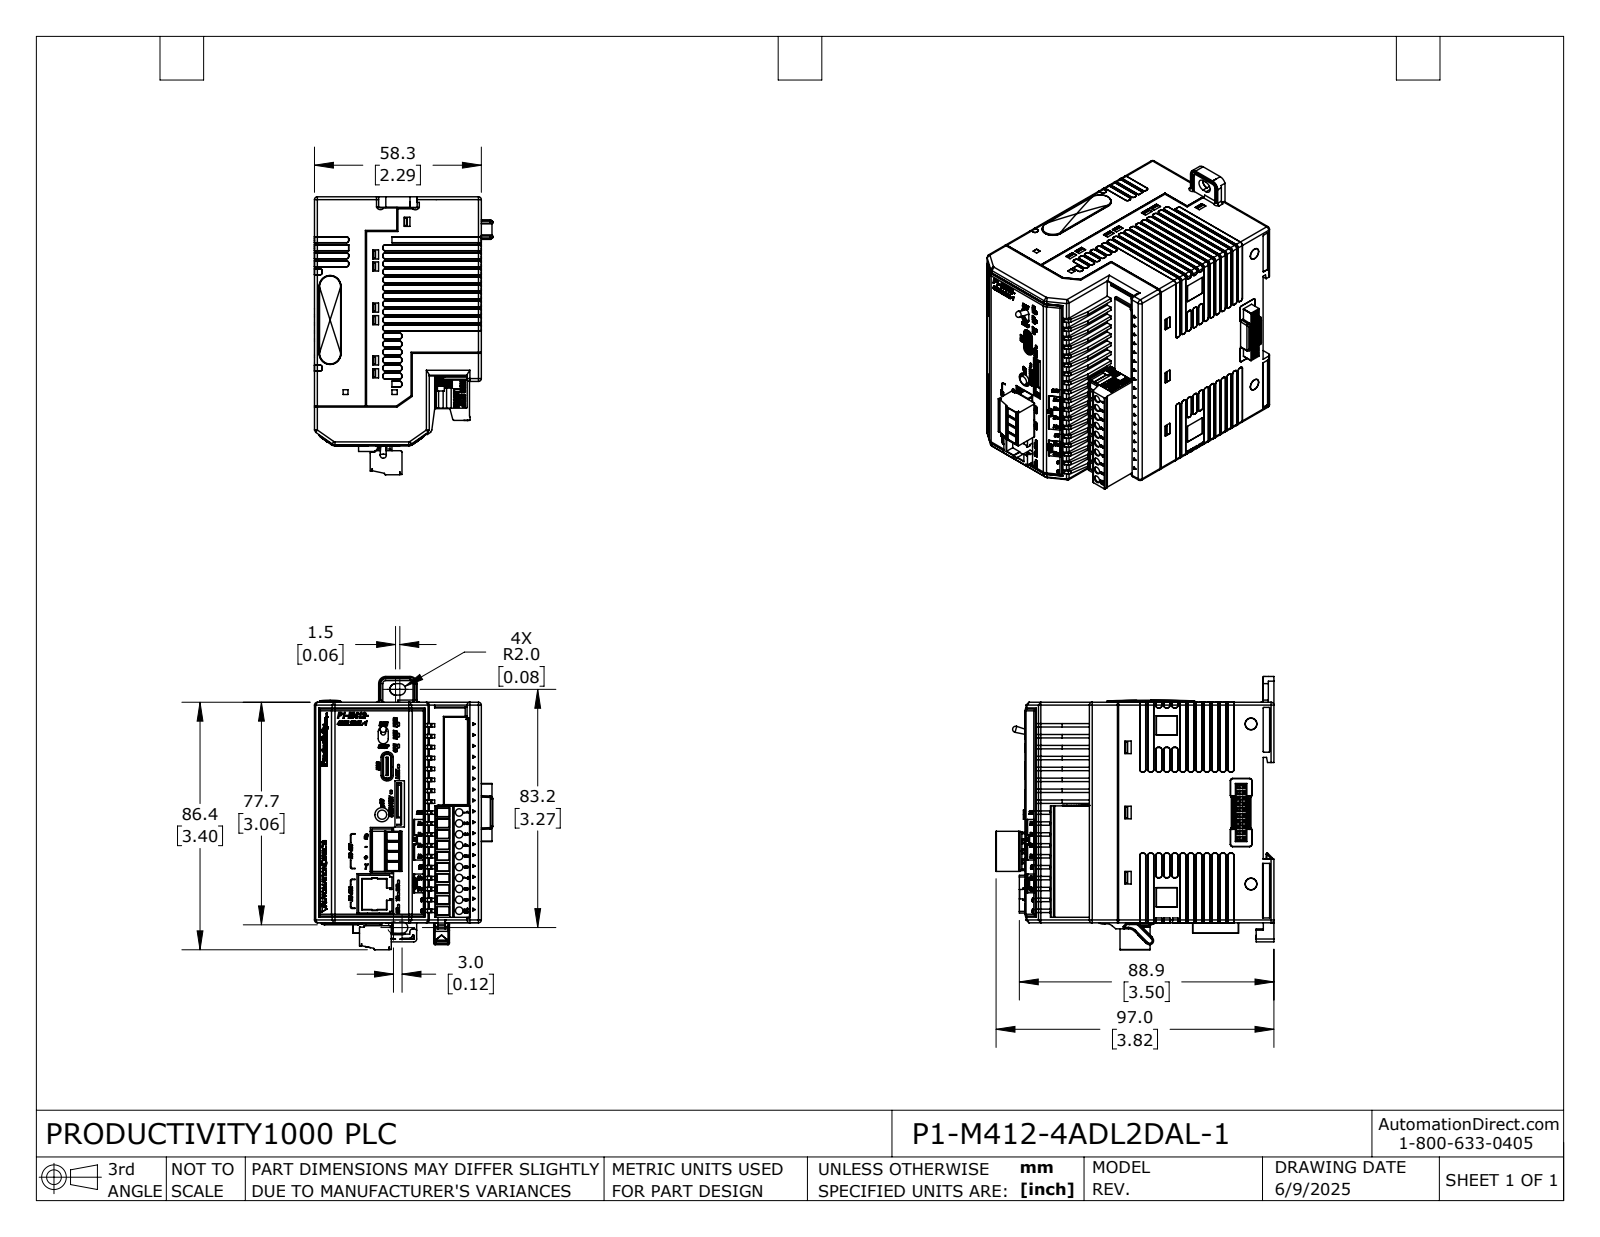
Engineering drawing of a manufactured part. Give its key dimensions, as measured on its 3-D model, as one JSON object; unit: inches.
{"part_name": "P1-M412-4ADL2DAL-1", "step_written_by": "SolidWorks 2024 (AUTOMOTIVE_DESIGN)", "units": "inches", "bodies": {"solids": 30, "faces": 3772, "planar": 2195, "cylindrical": 901, "other": 676}, "overall_size": [3.686, 3.593, 2.452], "volume_in3": 2.128, "surface_area_in2": 107, "round_holes": [[0.194, 1]], "round_bosses_or_shafts": [[0.214, 1], [0.126, 1]], "partial_cylinders_radius": [[0.01, 172], [0.008, 86], [0.02, 49], [0.039, 33], [0.079, 8], [0.024, 7], [0.004, 6], [0.012, 4]], "face_to_face_distances": [2.235, 0.02, 0.039, 2.275, 3.01, 3.022, 2.294, 2.294, 2.255, 3.02]}
